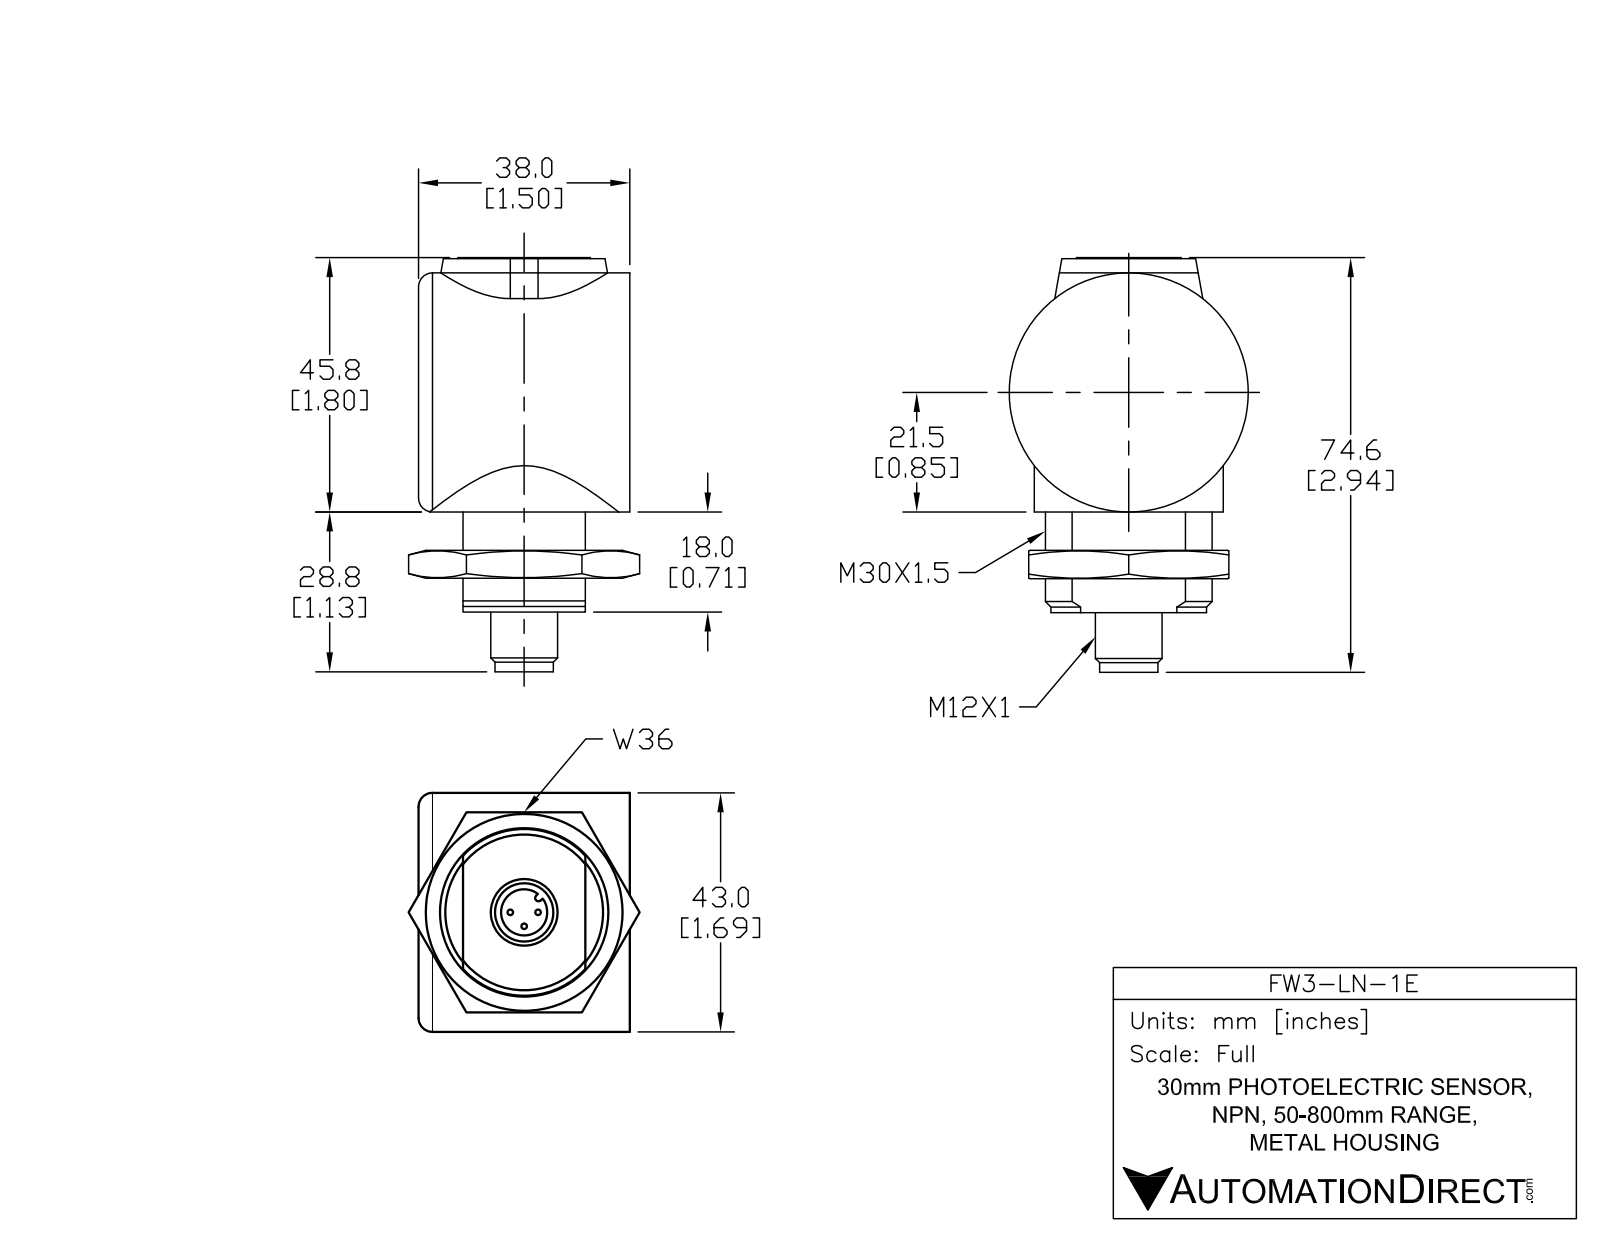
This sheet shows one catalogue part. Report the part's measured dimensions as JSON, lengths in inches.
{"part_name": "FW3-LN-1E", "step_written_by": "SolidWorks 2013 (AUTOMOTIVE_DESIGN)", "units": "inches", "bodies": {"solids": 1, "faces": 201, "planar": 111, "cylindrical": 35, "other": 55}, "overall_size": [2.928, 1.69, 1.49], "volume_in3": 4.301, "surface_area_in2": 19.68, "round_holes": [[0.172, 1], [0.315, 1], [1.58, 1]], "round_bosses_or_shafts": [[0.04, 3], [1.69, 1], [0.47, 1], [0.39, 1], [0.18, 1]], "partial_cylinders_radius": [[0.48, 2], [0.64, 2], [0.025, 1], [0.408, 1], [0.492, 1], [0.545, 1], [0.587, 1]], "face_to_face_distances": [1.44, 2.498, 0.11, 2.388, 0.3, 0.19, 2.198, 1.178, 0.262, 0.312], "hole_center_spacings": [0.349]}
